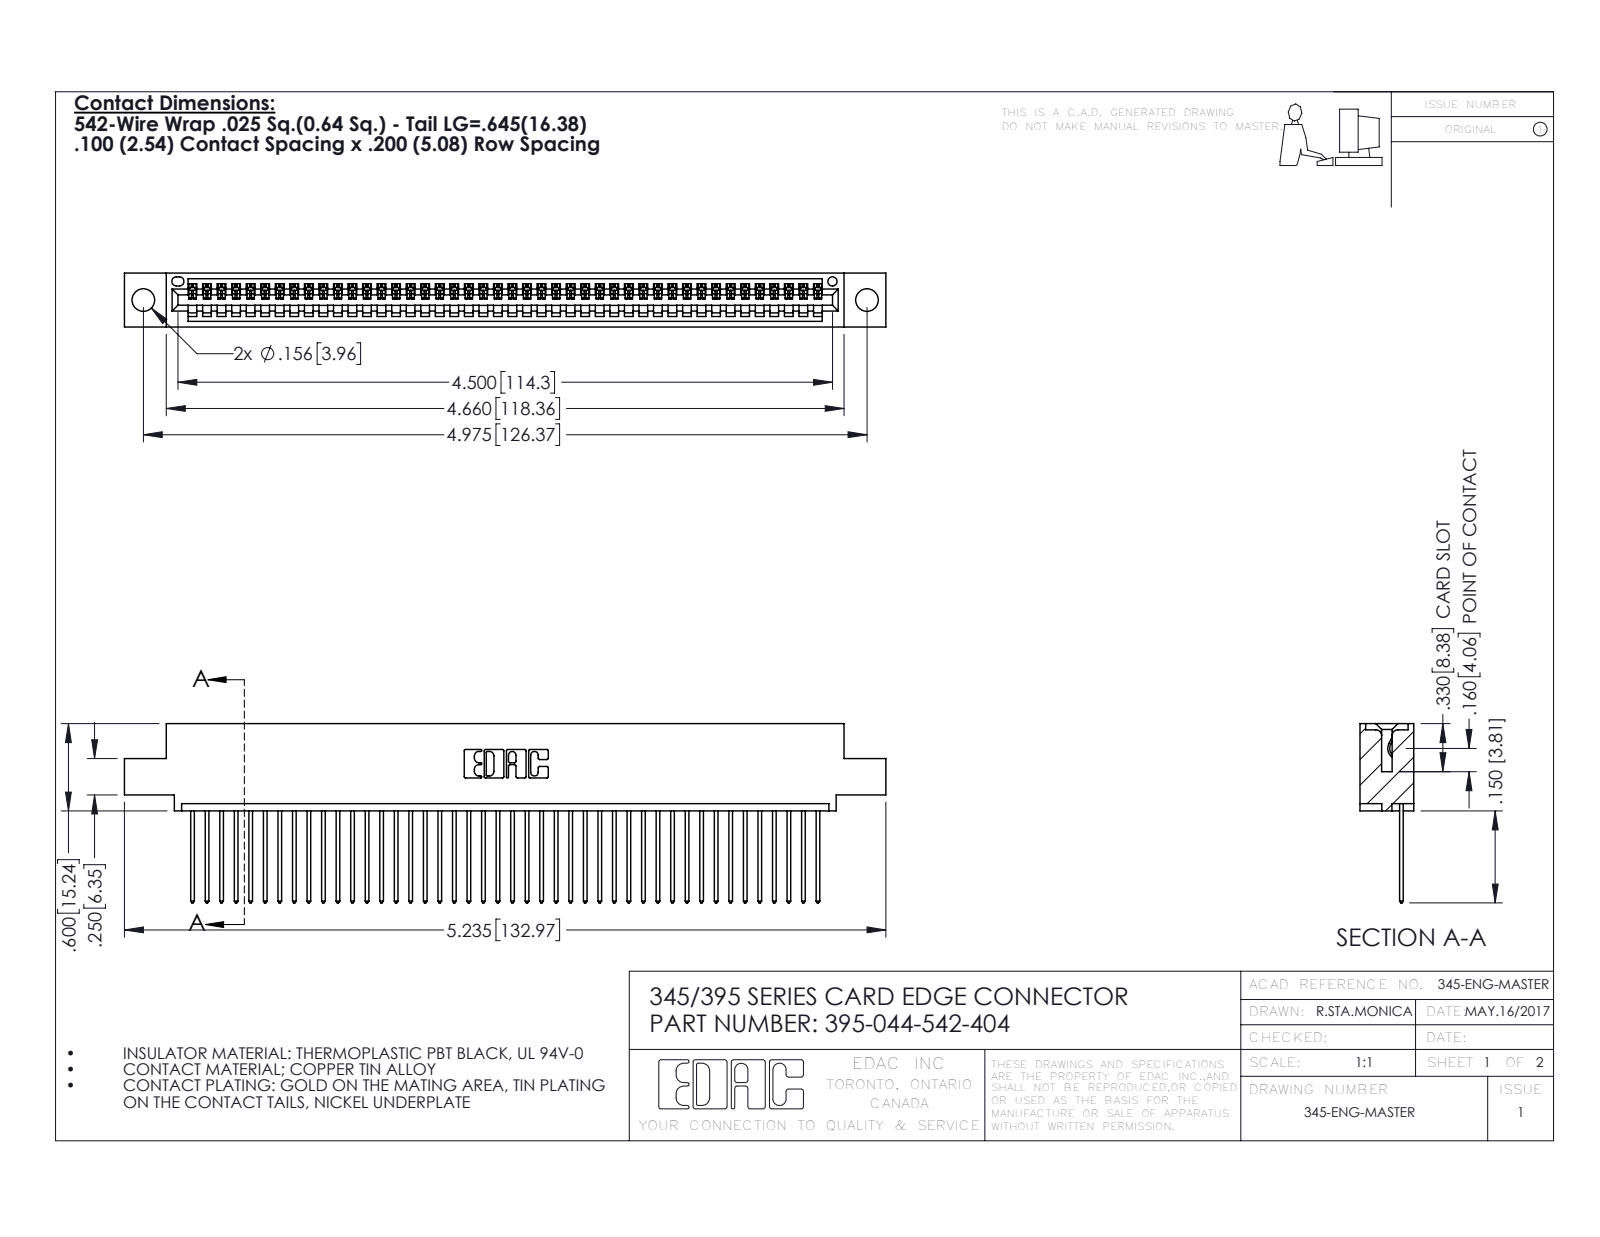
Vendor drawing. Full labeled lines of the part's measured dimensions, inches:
Part name (STEP PRODUCT): 345-292-001_345-293-142; 345 Part_0.110 Offset - 0.156 Dia-TH; 395-044-542-404
STEP written by: SolidWorks 2016 (CONFIG_CONTROL_DESIGN)
Units: inches
Bodies: 45 solids, 2682 faces (1844 planar, 838 cylindrical, 0 other)
Overall size (bounding box): 5.235 × 1.232 × 0.37
Volume: 0.768 in³ · Surface area: 26.75 in²
Round holes (diameter × count): ⌀0.156 ×2, ⌀0.064 ×1
Partial cylindrical surfaces — rounded edges, fillets, slot ends (radius × count): R0.006 ×88, R0.01 ×88, R0.01 ×22, R0.007 ×6, R0.031 ×6, R0.026 ×3, R0.031 ×2, R0.04 ×2
Main face-to-face distances: 0.072, 0.298, 0.37, 0.098, 0.272, 0.025, 0.2, 0.225, 0.149, 0.072
Hole centre spacings: 0.27, 4.739, 4.975
